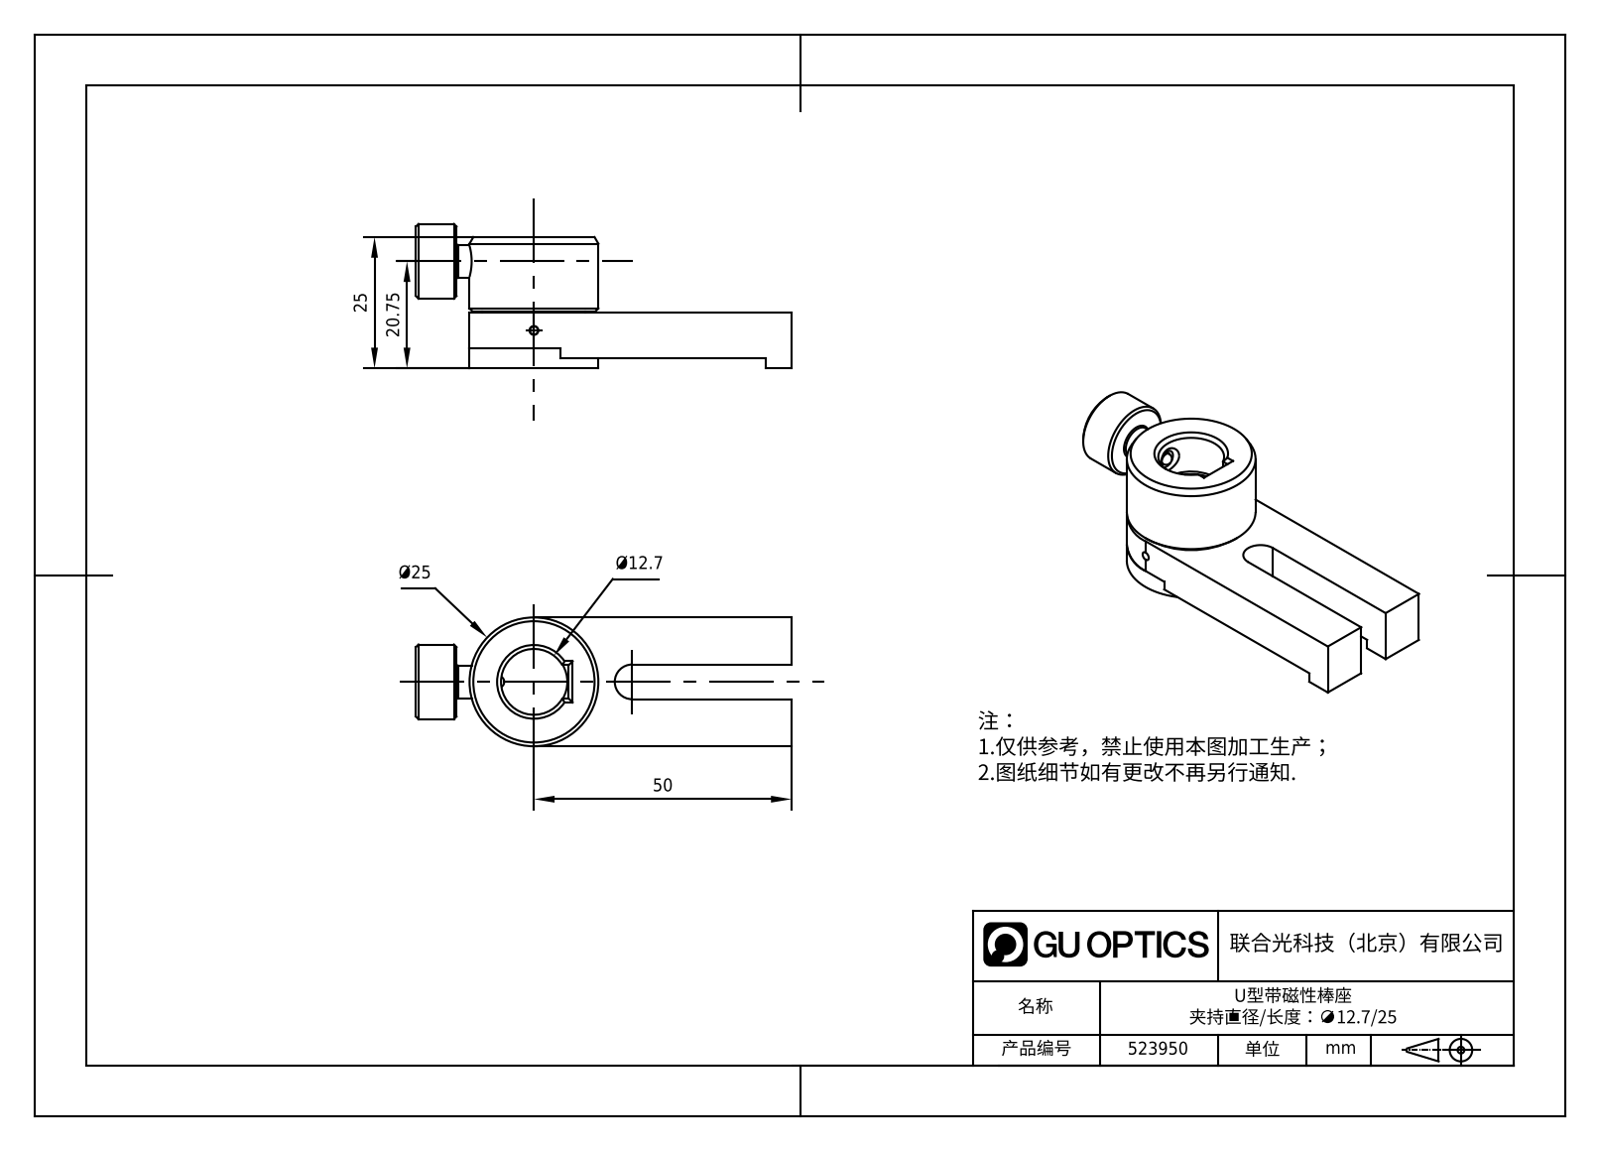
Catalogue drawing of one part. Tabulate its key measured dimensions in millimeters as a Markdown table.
| quantity | value |
| --- | --- |
| part name | 523950 |
| STEP written by | SolidWorks 2016 (CONFIG_CONTROL_DESIGN) |
| units | millimeters |
| bodies | 10 solids, 205 faces (64 planar, 82 cylindrical, 59 other) |
| overall size | 72.9 × 28.04 × 24.99 |
| volume | 17 228 mm³ |
| surface area | 11 125 mm² |
| round holes (diameter × count) | 4.83 × 3, 1.59 × 1, 1.7 × 1, 1.78 × 1, 2.15 × 1, 2.54 × 1, 3.17 × 1, 3.51 × 1, 4.62 × 1, 5.11 × 1, 12.78 × 1, 12.95 × 1 |
| round bosses / shafts (diameter × count) | 4.76 × 3, 24.99 × 1, 20.05 × 1, 17.78 × 1, 17.27 × 1, 14.48 × 1, 6.35 × 1, 3 × 1 |
| partial cylindrical surfaces (radius × count) | 3.37 × 1, 12.95 × 1 |
| main face-to-face distances | 8.89, 9.13, 15.87, 25, 1.83, 7.06, 1.98, 3.81, 10.87, 6.74 |
| hole center spacings | 16.5, 9.53, 9.52, 13.01 |
